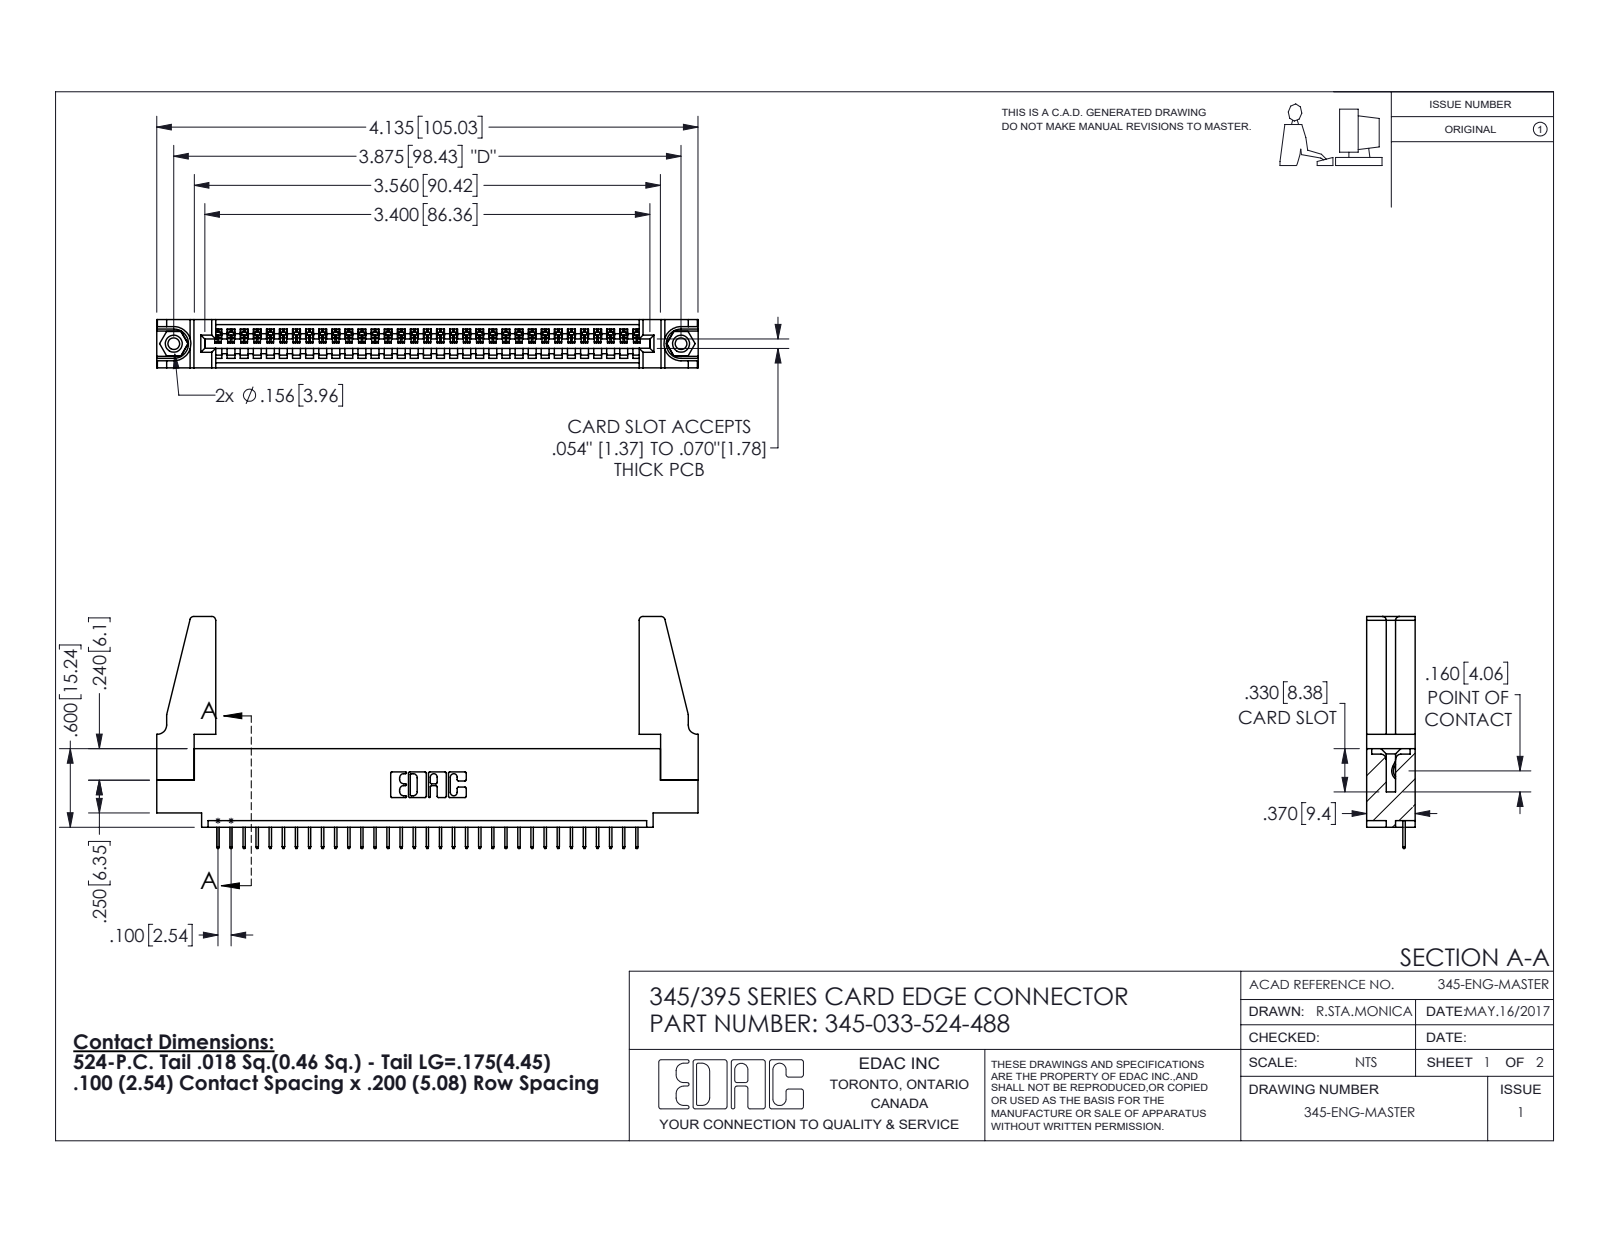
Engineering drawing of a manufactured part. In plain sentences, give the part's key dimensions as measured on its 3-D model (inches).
The part is named "345-292-001_345-293-124; 345-250-001_345-250-001-102; 345-033-524-488; 345-220-078_345-220-088 (+1 more)". Its 3-D file was written by "SolidWorks 2016 (CONFIG_CONTROL_DESIGN)". It is 38 solids with 2300 faces: 1674 planar, 610 cylindrical and 16 other. Overall it measures 4.136 by 1.772 by 0.37 inches. Its volume is 0.79 cubic inches and its surface area 24.12 square inches. Round holes: 2 of diameter 0.089, 2 of diameter 0.125, 2 of diameter 0.156, 1 of diameter 0.064. Round bosses or shafts: 2 of diameter 0.155. Partial cylindrical surfaces (rounded edges, fillets, slot ends): 66 of radius 0.006, 22 of radius 0.01, 8 of radius 0.03, 6 of radius 0.007, 6 of radius 0.031, 3 of radius 0.026, 2 of radius 0.031, 2 of radius 0.04. The main face-to-face distances are 0.072, 0.37, 0.298, 0.2, 0.098, 0.272, 0.025, 0.225, 0.072, 0.149. The hole center spacings are 0.27, 3.64, 3.875.
